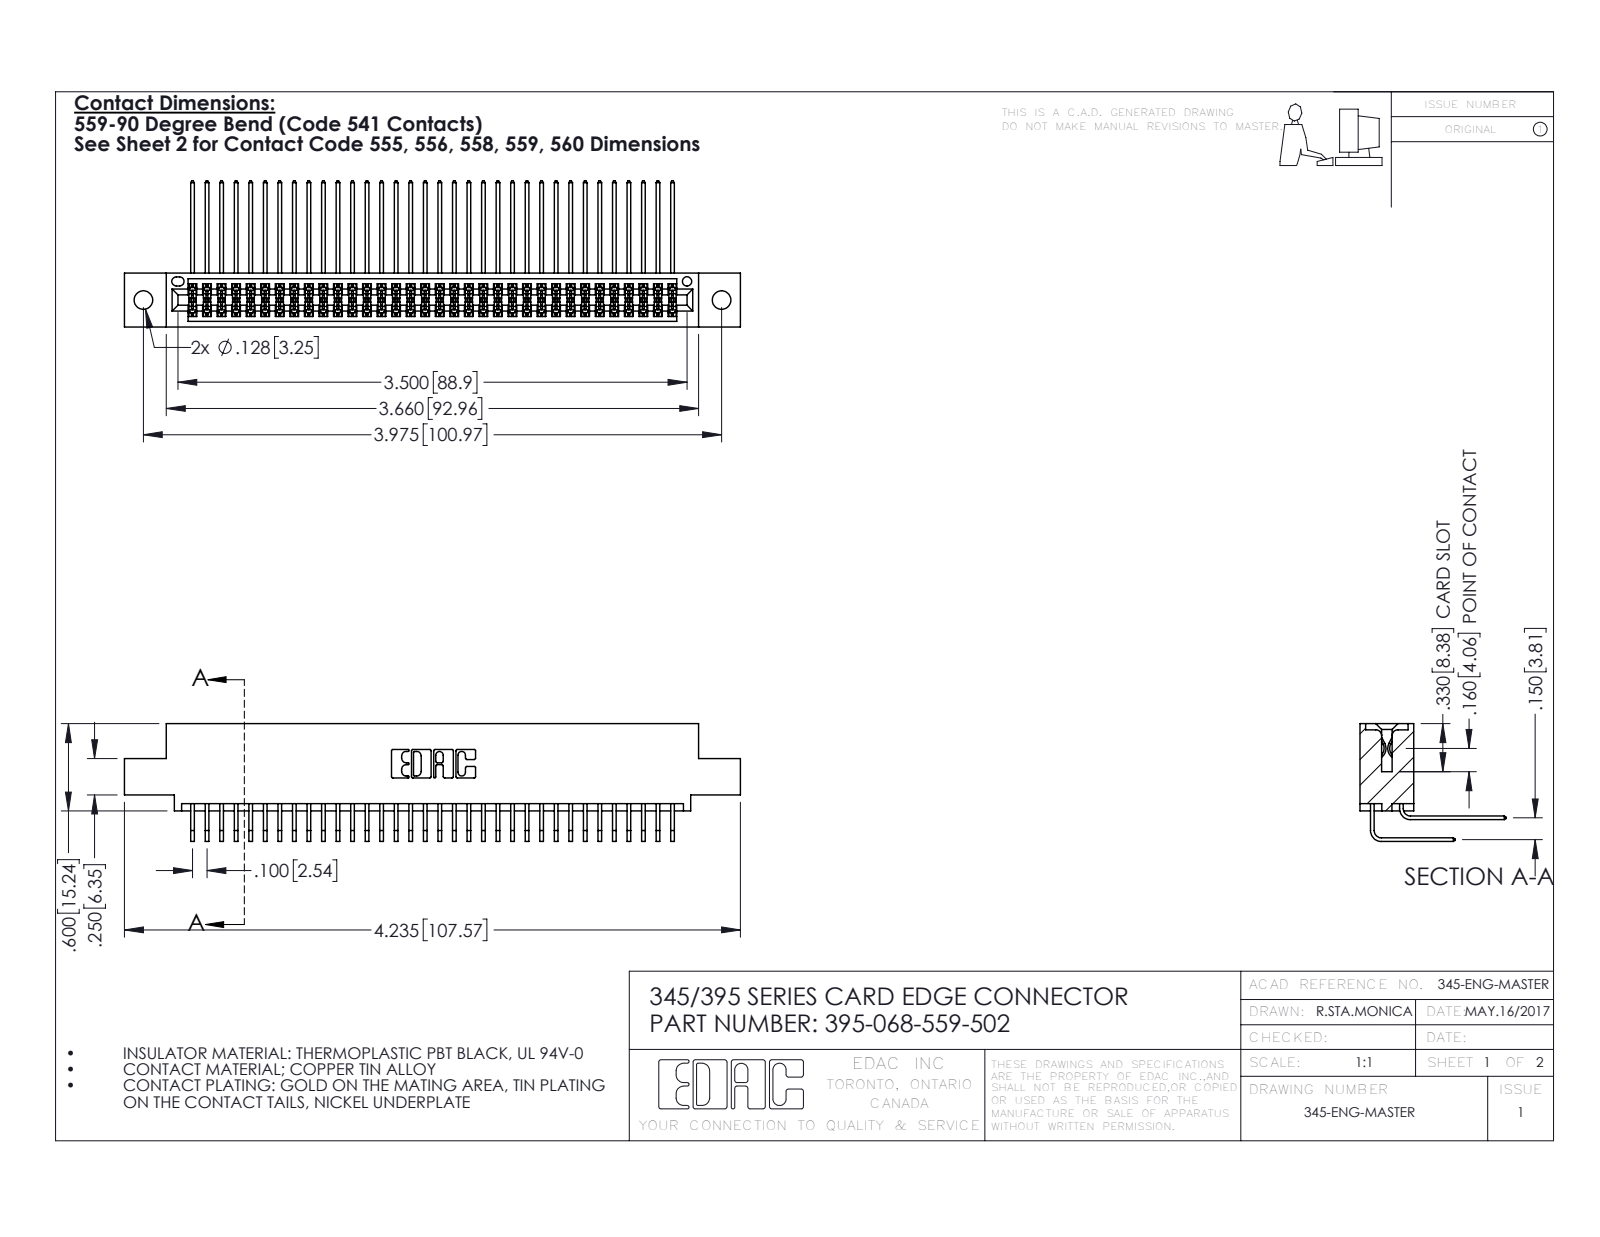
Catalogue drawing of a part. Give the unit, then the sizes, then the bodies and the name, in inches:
Units: inches
Overall size (bounding box): 4.235 × 1.005 × 0.809
Round holes (diameter × count): ⌀0.128 ×2, ⌀0.064 ×1
Partial cylindrical surfaces — rounded edges, fillets, slot ends (radius × count): R0.006 ×103, R0.01 ×22, R0.007 ×6, R0.031 ×6, R0.026 ×3, R0.014 ×2, R0.019 ×2, R0.022 ×2
Main face-to-face distances: 0.072, 0.298, 0.2, 0.37, 0.098, 0.272, 0.025, 0.225, 0.175, 0.15
Hole centre spacings: 0.27, 3.74, 3.975
Volume: 0.65 in³ · Surface area: 26.76 in²
Bodies: 69 solids, 3666 faces (2464 planar, 1202 cylindrical, 0 other)
Part name (STEP PRODUCT): 345-292-001_559 Tail - 2; 345 Part_0.110 Offset - 0.128 Dia; 395-068-559-502; 345-292-001_558 559 Tail - 1
STEP written by: SolidWorks 2016 (CONFIG_CONTROL_DESIGN)
